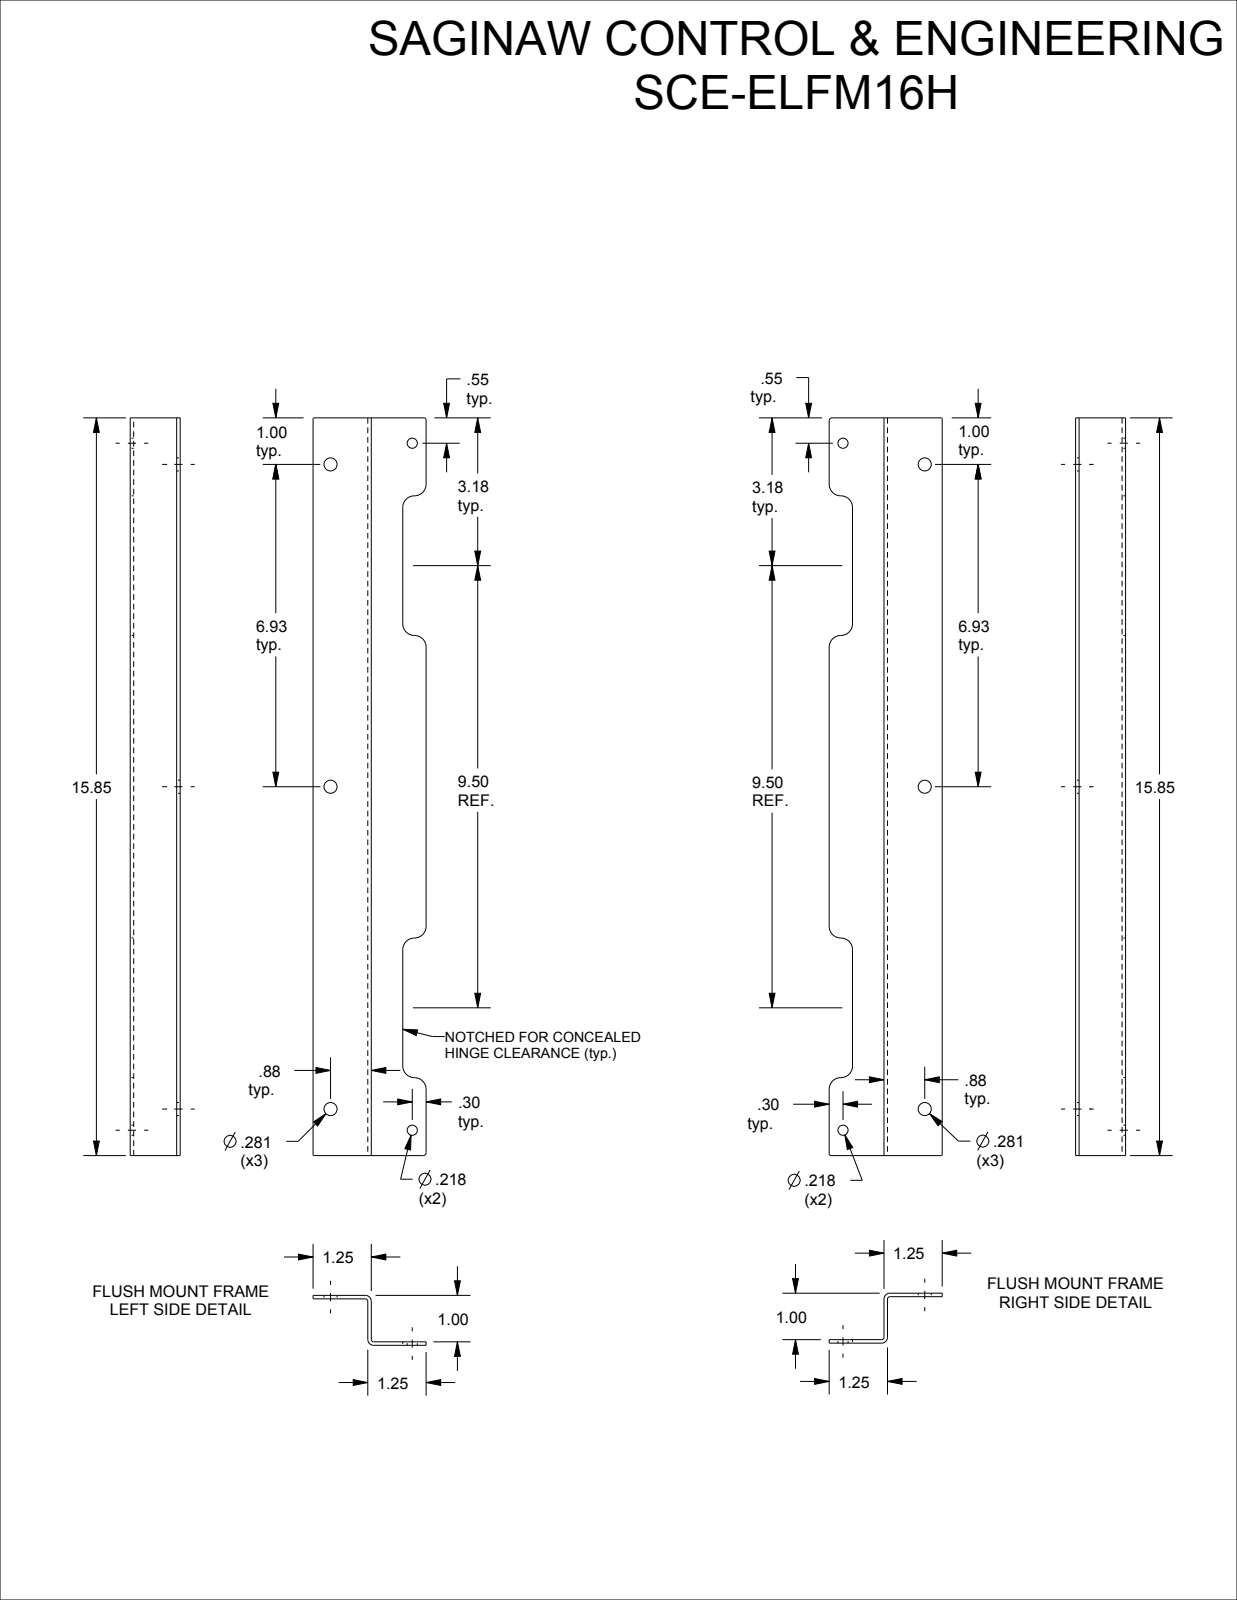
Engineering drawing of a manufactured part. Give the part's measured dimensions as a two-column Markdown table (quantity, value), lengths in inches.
| quantity | value |
| --- | --- |
| part name | SCE-ELFM16H |
| STEP written by | SolidWorks 2019 (CONFIG_CONTROL_DESIGN) |
| units | inches |
| bodies | 2 solids, 78 faces (36 planar, 42 cylindrical, 0 other) |
| overall size | 19 × 15.85 × 1.073 |
| volume | 7.472 in³ |
| surface area | 205.8 in² |
| round holes (diameter × count) | 0.281 × 6, 0.218 × 4 |
| partial cylindrical surfaces (radius × count) | 0.25 × 16, 0.015 × 4, 0.051 × 4, 0.126 × 4, 0.04 × 2, 0.062 × 2 |
| main face-to-face distances | 0.075, 0.075, 0.923, 0.998, 0.998, 1.073, 16.575, 16.65, 16.5, 16.575 |
| hole center spacings | 1.813, 6.925, 7.586, 14.412, 16.501, 18.07, 19.52, 21.833 |
